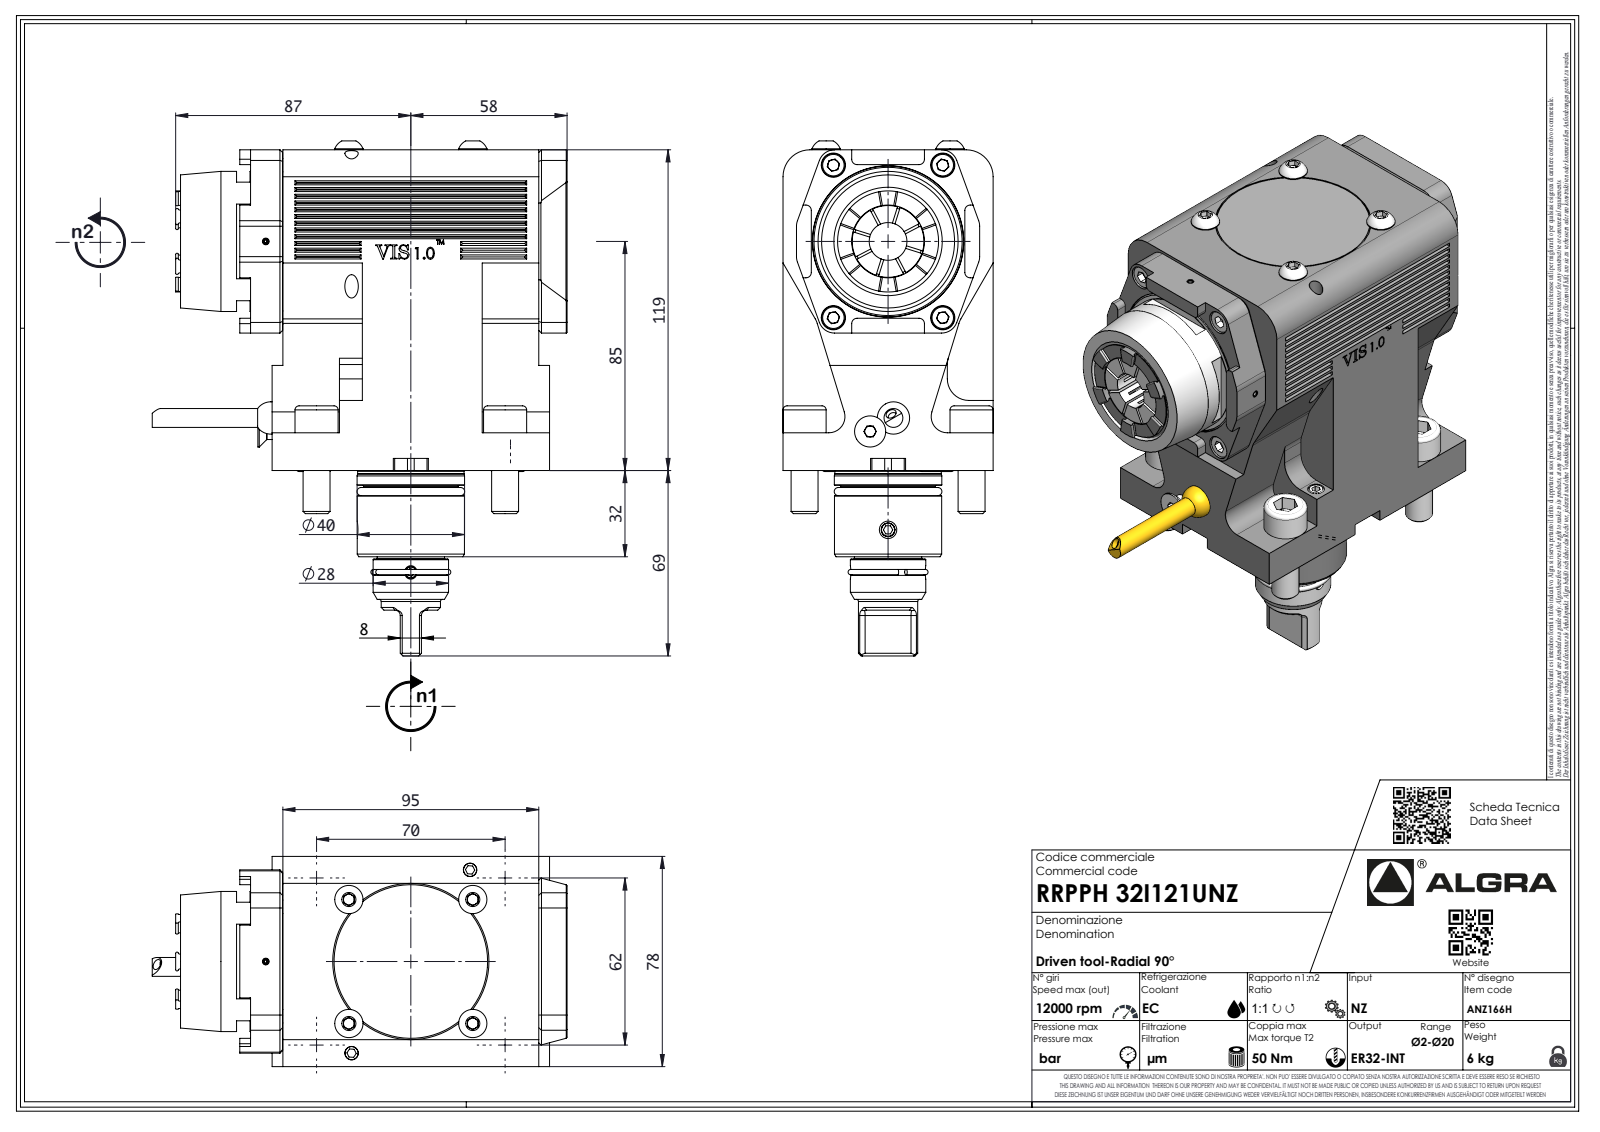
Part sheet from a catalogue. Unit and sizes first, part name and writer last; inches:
Units: inches
Overall size (bounding box): 7.394 × 5.741 × 3.071
Round holes (diameter × count): ⌀0.083 ×1, ⌀0.236 ×1
Round bosses / shafts (diameter × count): ⌀2.047 ×1, ⌀1.571 ×1, ⌀1.567 ×1, ⌀1.555 ×1, ⌀1.382 ×1, ⌀1.378 ×1, ⌀1.102 ×1, ⌀0.984 ×1
Partial cylindrical surfaces — rounded edges, fillets, slot ends (radius × count): R0.197 ×16, R0.079 ×14, R0.236 ×10, R0.013 ×7, R0.02 ×7, R0.146 ×7, R0.315 ×6, R0.394 ×2
Main face-to-face distances: 3.071, 4.685, 0.157, 4.173, 3.898, 0.472, 0.984, 4.177, 0.827, 2.913
Volume: 61.02 in³ · Surface area: 131.9 in²
Bodies: 1 solid, 611 faces (376 planar, 105 cylindrical, 130 other)
Part name (STEP PRODUCT): RRPPH32I121UNZ
STEP written by: SolidWorks 2023 (AUTOMOTIVE_DESIGN)
